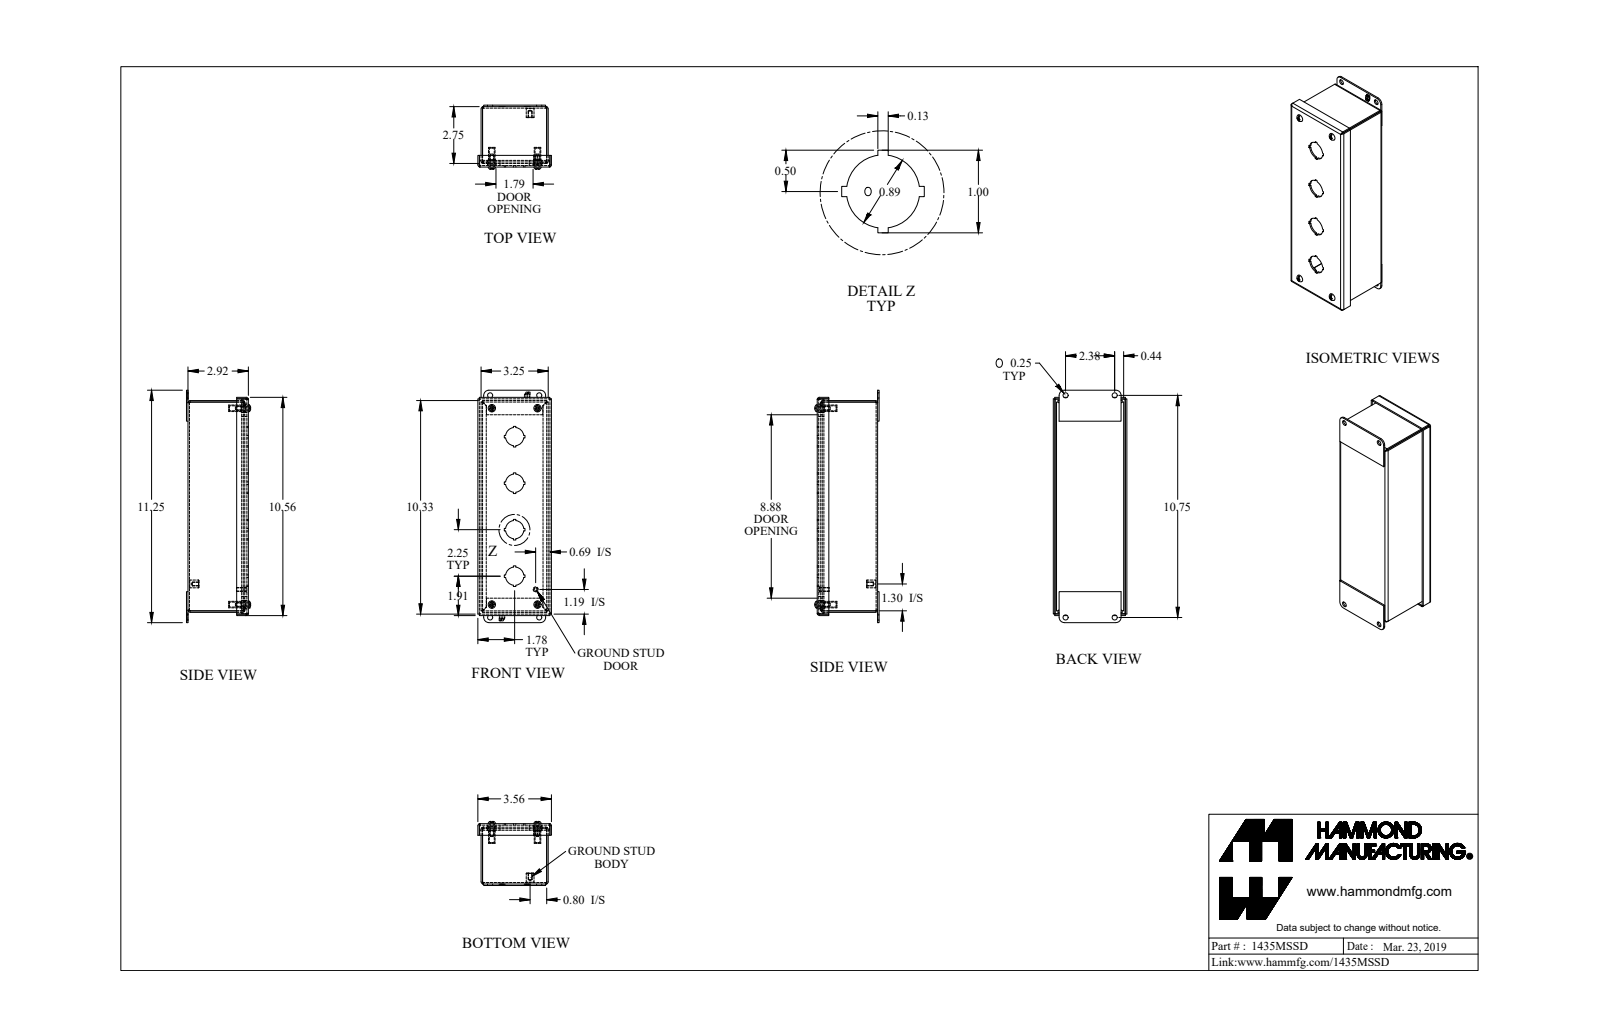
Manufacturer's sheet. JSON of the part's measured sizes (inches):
{"part_name": "1435MSSD_Default", "step_written_by": "SolidWorks 2019 (CONFIG_CONTROL_DESIGN)", "units": "inches", "bodies": {"solids": 19, "faces": 509, "planar": 331, "cylindrical": 148, "other": 30}, "overall_size": [11.25, 3.562, 3.104], "volume_in3": 14.77, "surface_area_in2": 385.7, "round_holes": [[0.25, 8], [0.065, 4], [0.239, 4], [0.253, 4], [0.406, 4], [0.886, 4], [0.156, 1]], "round_bosses_or_shafts": [[0.19, 5], [0.406, 4], [0.315, 4], [0.148, 4], [0.375, 1], [0.25, 1]], "partial_cylinders_radius": [[0.036, 12], [0.108, 12], [0.171, 4], [0.25, 4]], "face_to_face_distances": [0.072, 2.85, 0.072, 3.178, 2.922, 2.778, 3.25, 3.106, 10.178, 0.156], "hole_center_spacings": [8.2, 9.5, 10.126, 10.381, 9.754, 0.63, 0.631, 1.764]}
